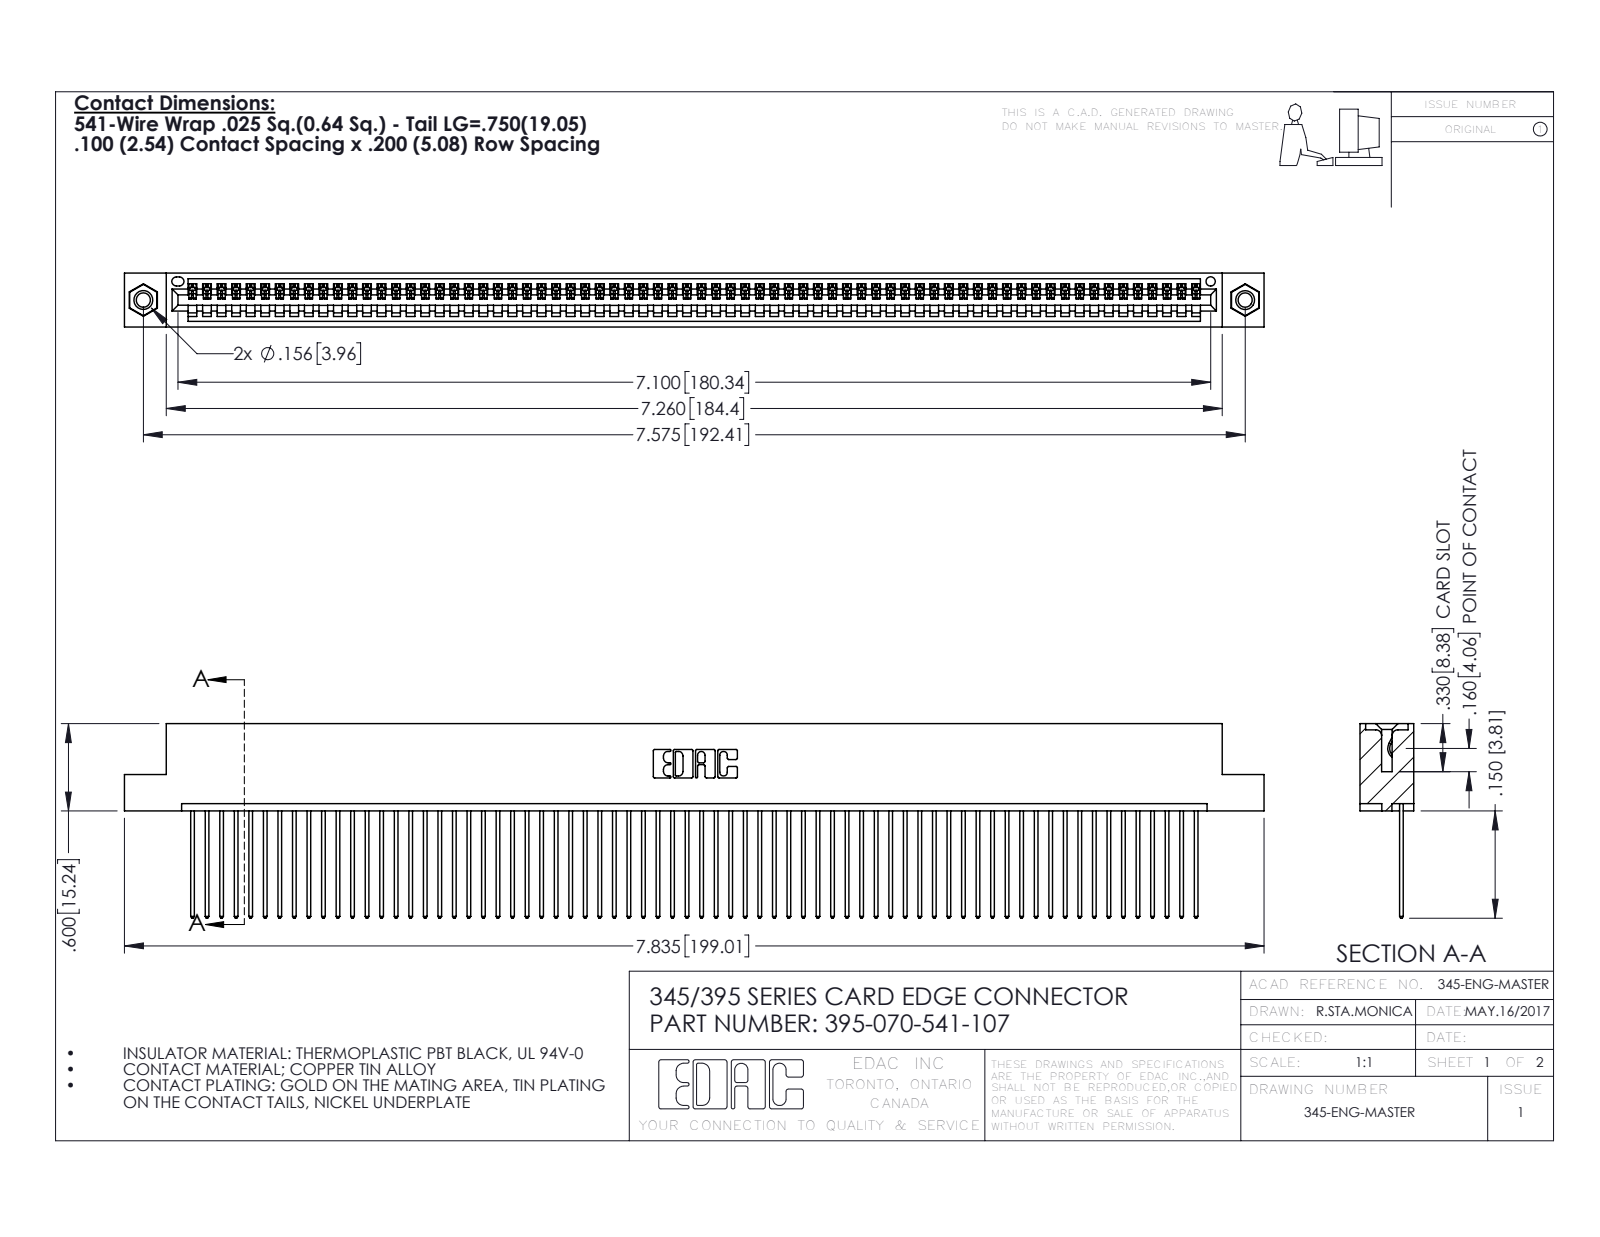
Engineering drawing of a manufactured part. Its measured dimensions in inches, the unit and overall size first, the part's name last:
Units: inches
Overall size (bounding box): 7.835 × 1.337 × 0.37
Round holes (diameter × count): ⌀0.098 ×2, ⌀0.125 ×2, ⌀0.156 ×2, ⌀0.064 ×1
Round bosses / shafts (diameter × count): ⌀0.155 ×2
Partial cylindrical surfaces — rounded edges, fillets, slot ends (radius × count): R0.006 ×140, R0.01 ×140, R0.01 ×22, R0.007 ×6, R0.031 ×6, R0.026 ×3, R0.031 ×2, R0.04 ×2
Main face-to-face distances: 0.072, 0.298, 0.098, 0.272, 0.025, 0.37, 0.2, 0.225, 0.149, 0.072
Hole centre spacings: 0.27, 7.339, 7.575
Volume: 1.181 in³ · Surface area: 42.6 in²
Bodies: 73 solids, 4246 faces (2912 planar, 1318 cylindrical, 16 other)
Part name (STEP PRODUCT): 345-292-001_345-293-141; 345-250-001_345-250-005-103; 345 Part_Flush Mounting Lugs - 0.156 Dia-TI; 395-070-541-107
STEP written by: SolidWorks 2016 (CONFIG_CONTROL_DESIGN)
